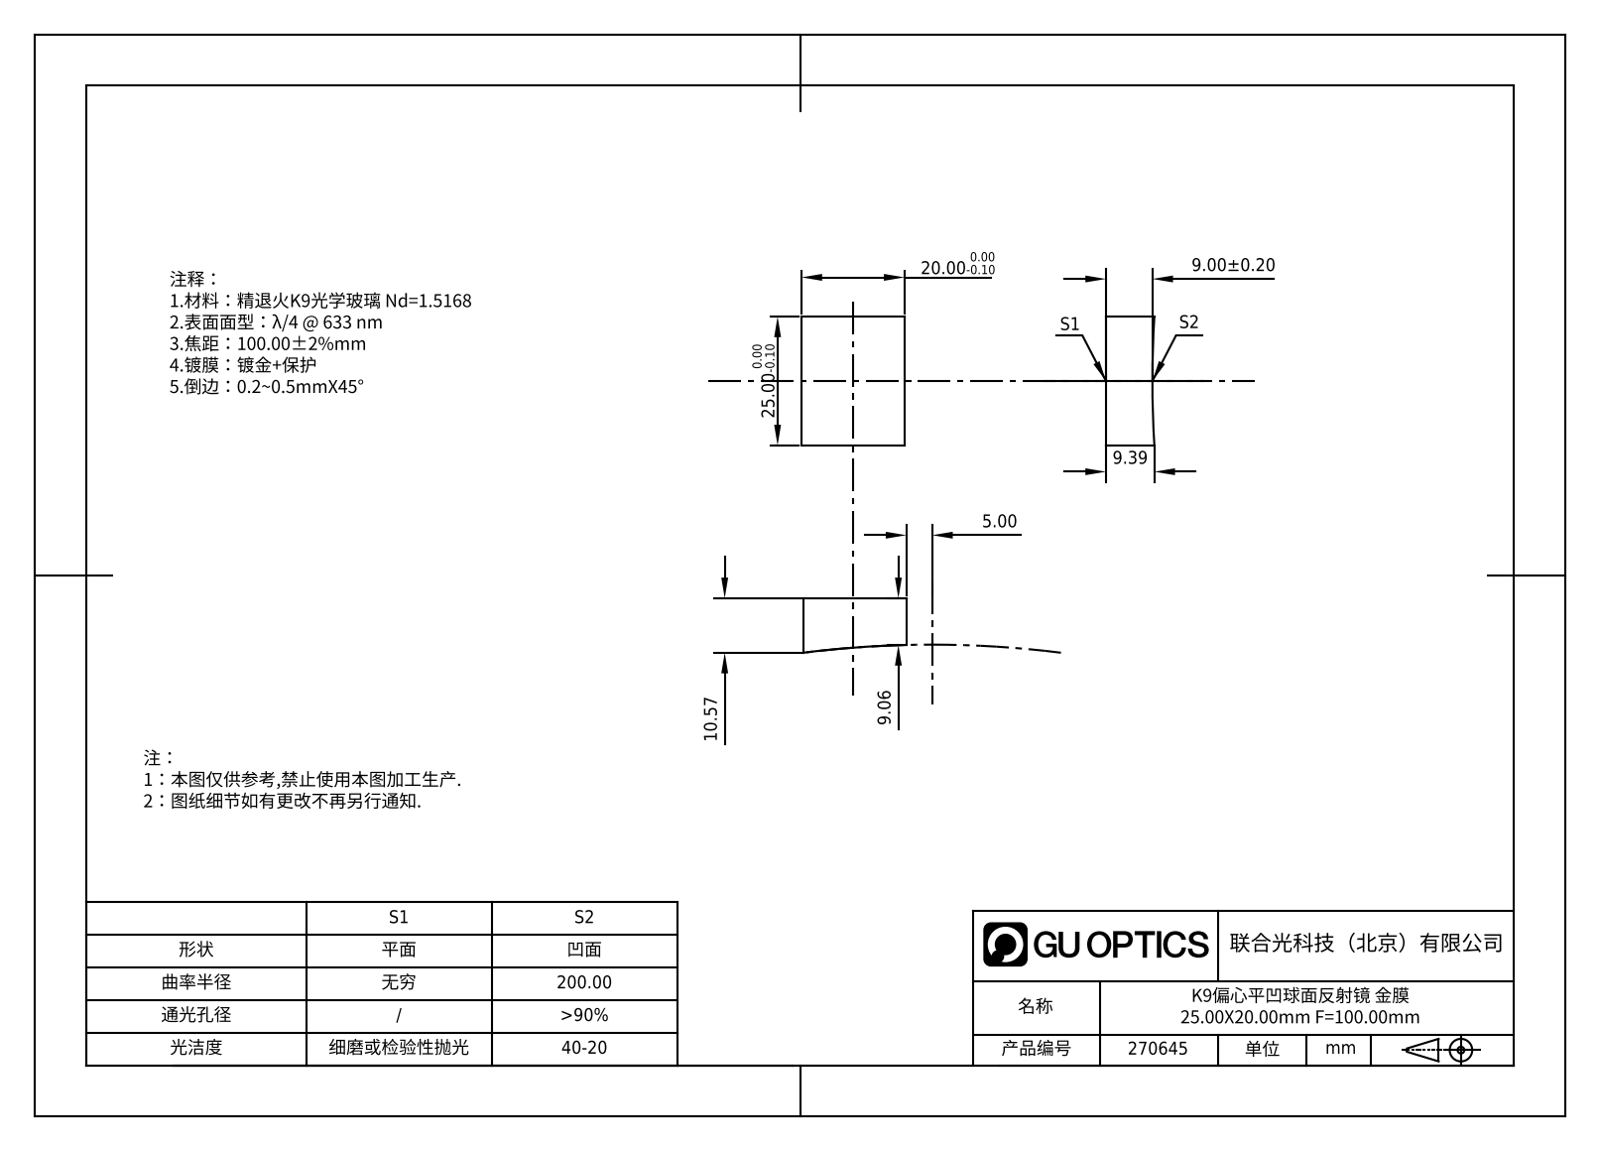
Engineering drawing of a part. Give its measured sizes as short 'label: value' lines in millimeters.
name: 270645
written by: SolidWorks 2020 (CONFIG_CONTROL_DESIGN)
unit: mm
bodies: 1 solid, 7 faces (5 planar, 0 cylindrical, 2 other)
size: 25 × 20 × 10.96
volume: 4 889 mm³; area: 1 901 mm²
face distances: 20, 25
